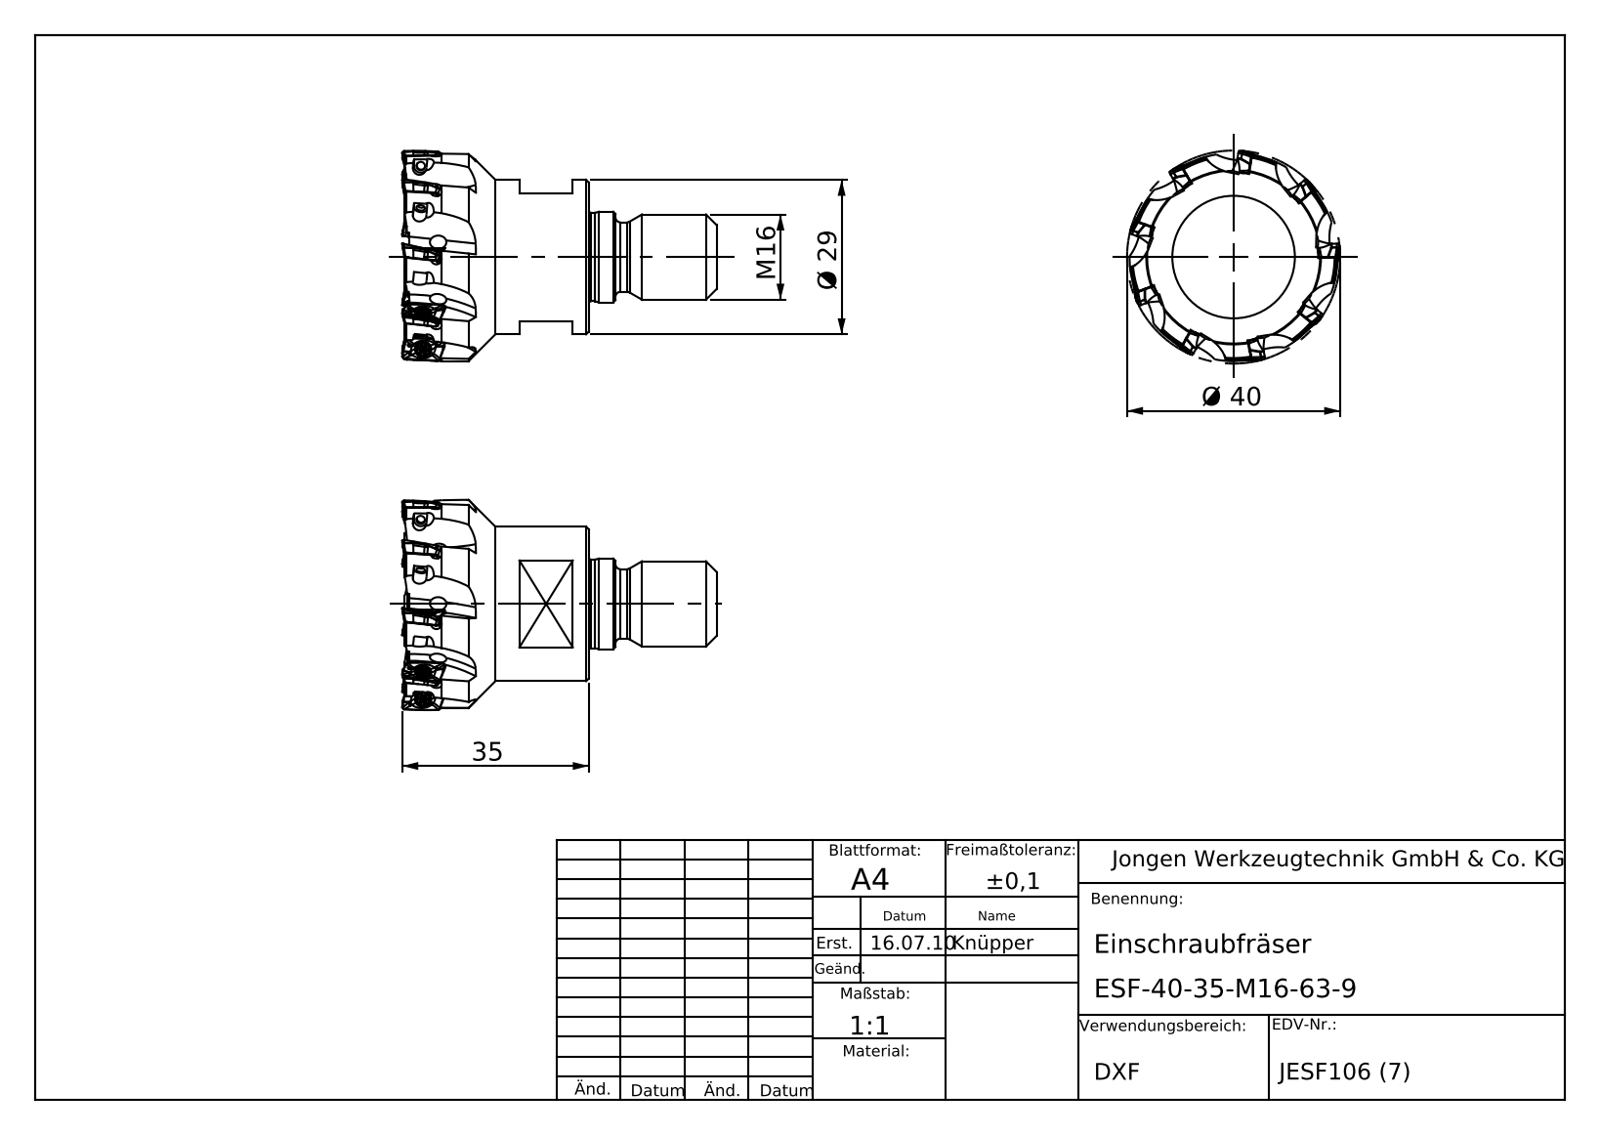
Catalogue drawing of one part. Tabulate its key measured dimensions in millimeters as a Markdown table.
| quantity | value |
| --- | --- |
| part name | ESF-40-35-M16-63-9 |
| STEP written by | SolidWorks 2011 (AUTOMOTIVE_DESIGN) |
| units | millimeters |
| bodies | 1 solid, 223 faces (74 planar, 49 cylindrical, 100 other) |
| overall size | 59 × 40 × 40 |
| volume | 31 601 mm³ |
| surface area | 10 121 mm² |
| round holes (diameter × count) | 2.5 × 9, 4 × 1 |
| round bosses / shafts (diameter × count) | 29 × 1, 17 × 1, 16.6 × 1, 16 × 1, 13 × 1 |
| partial cylindrical surfaces (radius × count) | 20 × 9, 19.53 × 1 |
| main face-to-face distances | 33.15, 24, 34.5, 1.35, 57.15, 58.5, 27, 37, 3, 13 |
